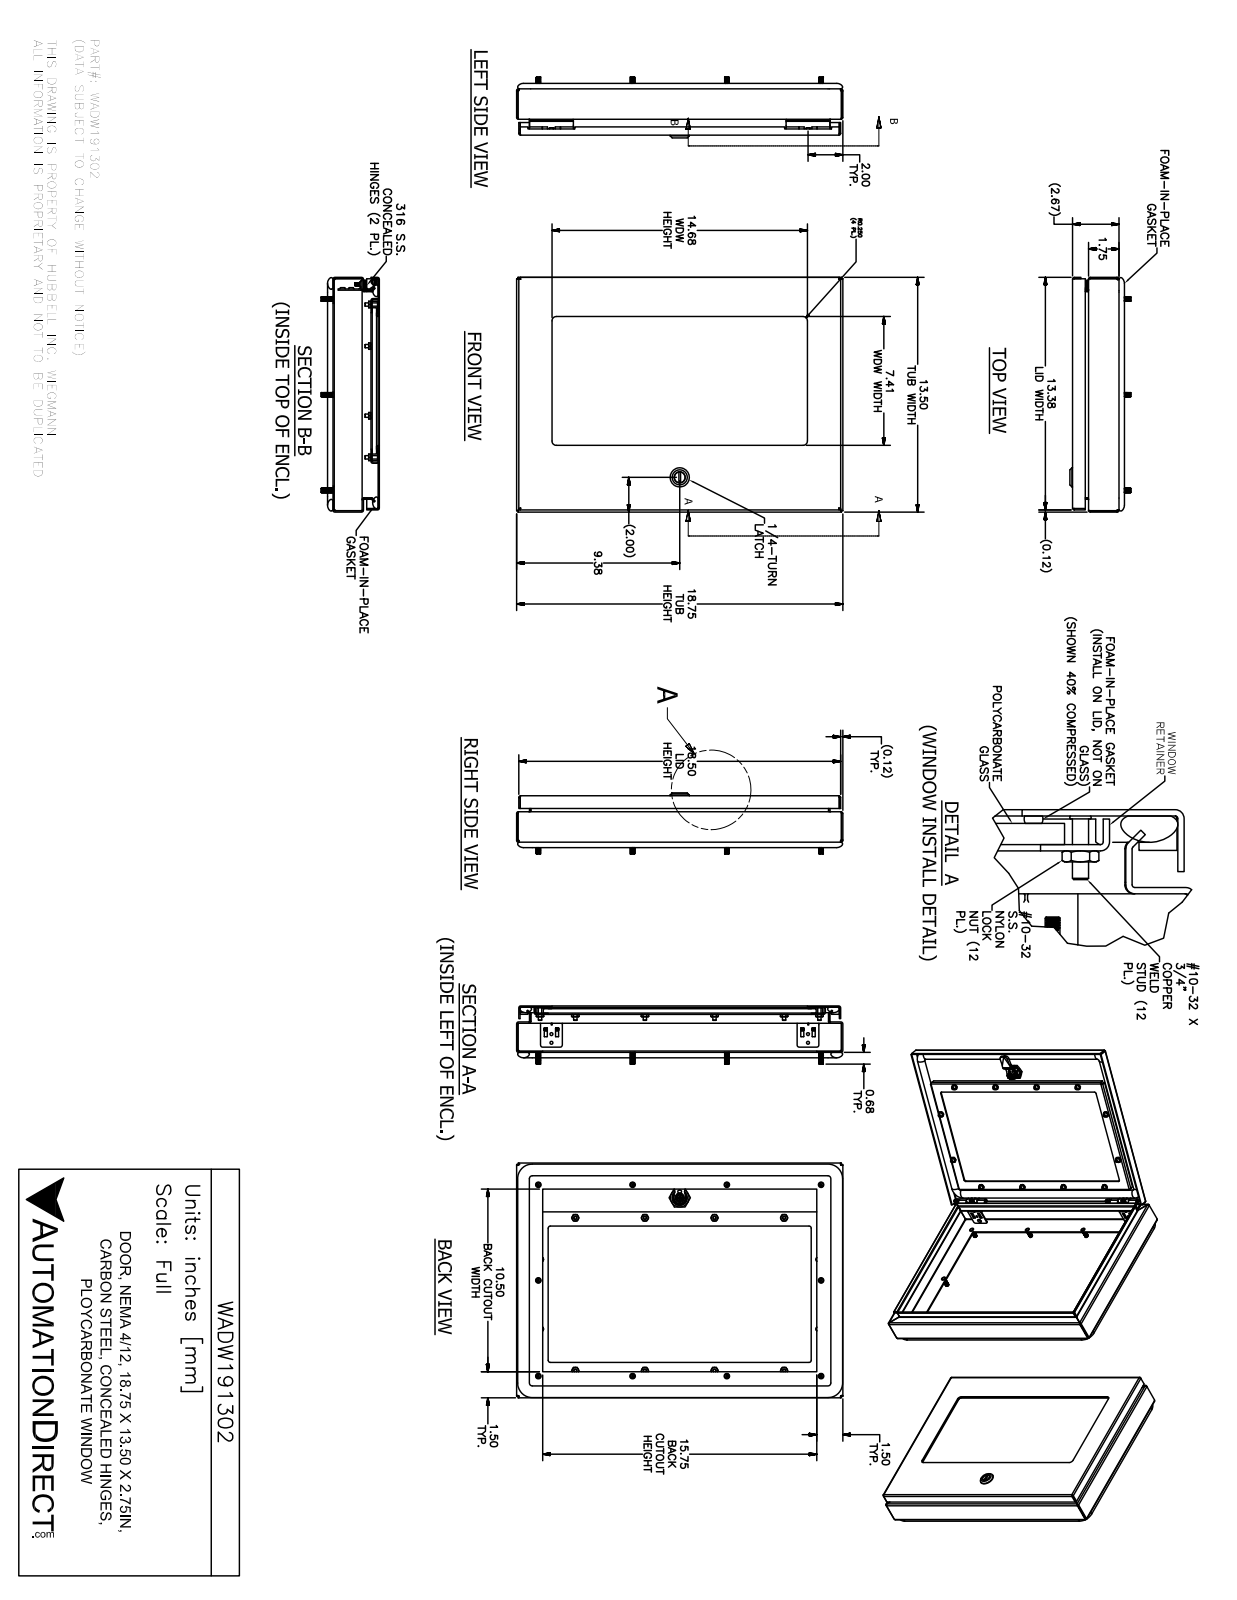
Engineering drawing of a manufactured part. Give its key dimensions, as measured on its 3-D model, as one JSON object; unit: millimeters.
{"part_name": "WADW191302", "step_written_by": "SolidWorks 2017 (AUTOMOTIVE_DESIGN)", "units": "millimeters", "bodies": {"solids": 65, "faces": 1951, "planar": 724, "cylindrical": 625, "other": 602}, "overall_size": [476.3, 342.9, 88.9], "volume_mm3": 1544000, "surface_area_mm2": 1001000, "round_holes": [[4, 14], [7.1, 12], [6.3, 9], [2.4, 4], [3.9, 4], [4.2, 4], [4.4, 4], [4.8, 4], [4.7, 1], [5, 1], [8, 1], [10, 1]], "round_bosses_or_shafts": [[6.4, 20], [4.8, 12], [9.1, 4], [8.1, 4], [6.5, 4], [4.2, 4], [3.3, 4], [28, 1]], "partial_cylinders_radius": [[0.8, 34], [0.3, 30], [1.3, 26], [2.7, 24], [3.2, 20], [0.4, 18], [0.5, 13], [0.8, 8]], "face_to_face_distances": [1.9, 10.4, 8.6, 6.4, 2.2, 4.1, 65.9, 55.4, 42.6, 61.8], "hole_center_spacings": [101.6, 245.2, 374.5, 139.7, 170.3, 203.2, 223.1, 301.2]}
